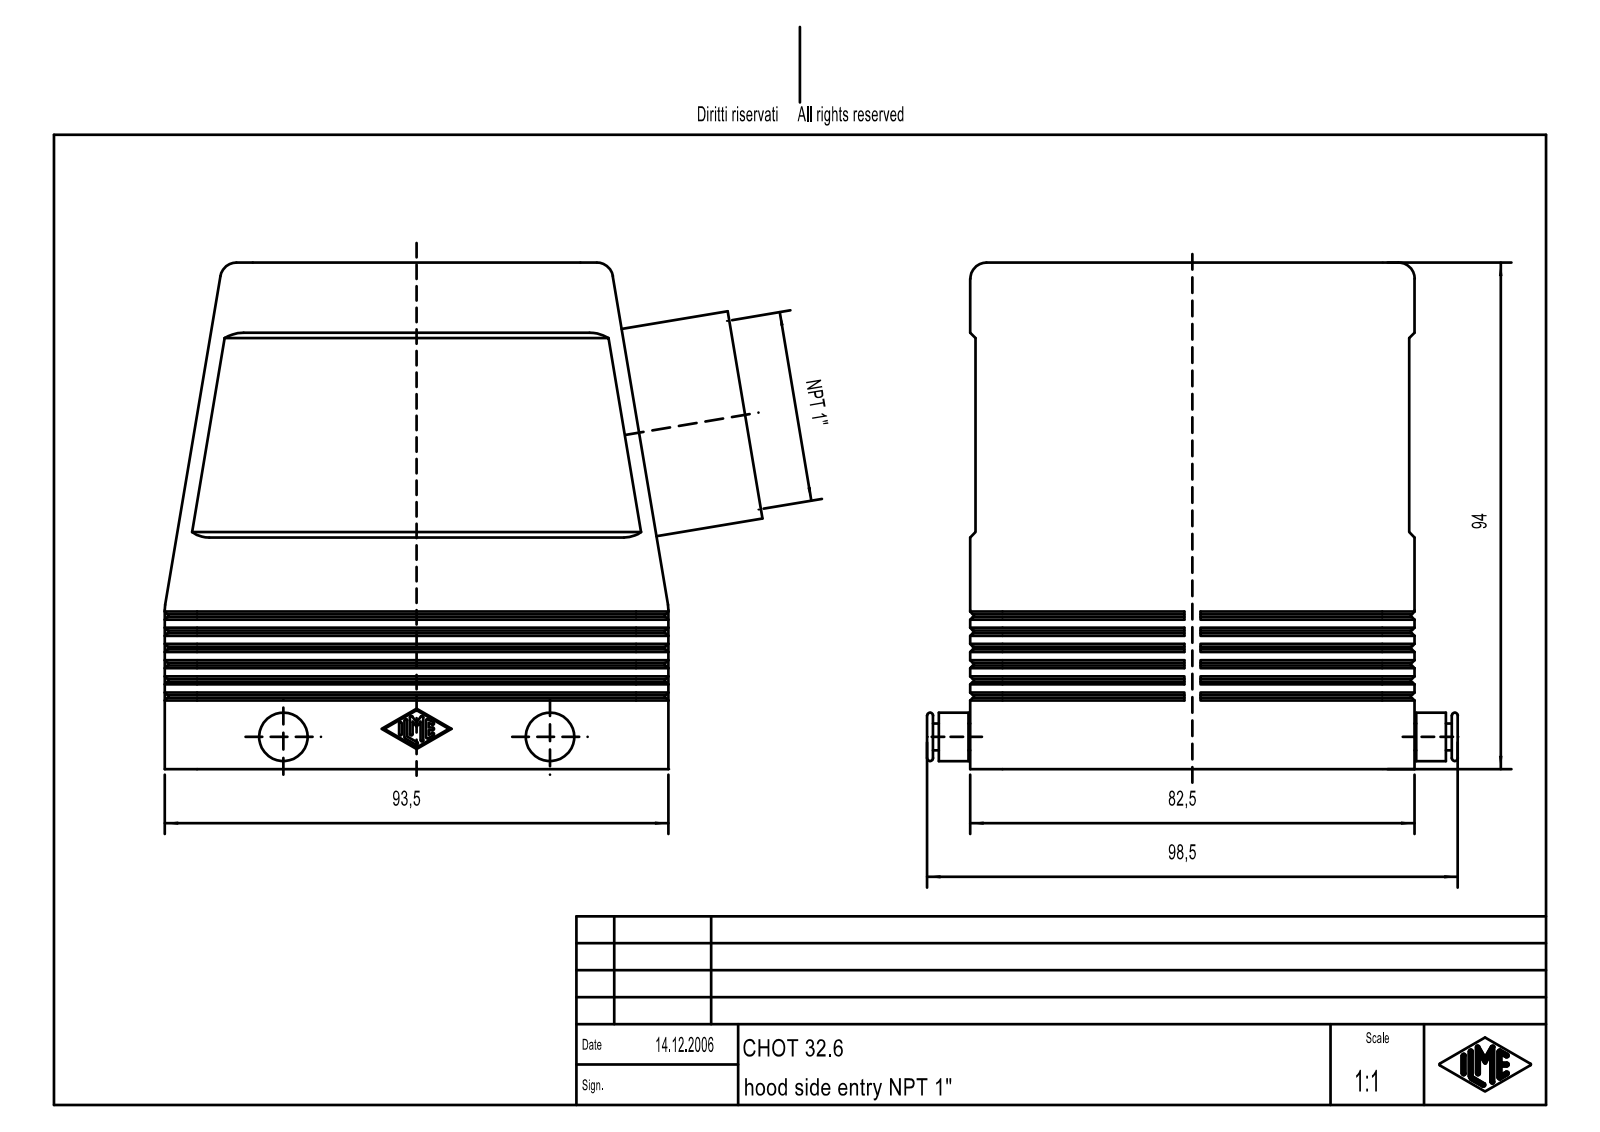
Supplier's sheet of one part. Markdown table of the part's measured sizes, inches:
| quantity | value |
| --- | --- |
| part name | MSBO10311 |
| STEP written by | Creo Elements/Direct Modeling 18.0B 02-Dec-2011 (C) Parametric Technology GmbH (AUTOMOTIVE_DESIGN) |
| units | inches |
| bodies | 1 solid, 519 faces (273 planar, 148 cylindrical, 98 other) |
| overall size | 4.369 × 3.878 × 3.701 |
| volume | 9.535 in³ |
| surface area | 123 in² |
| round holes (diameter × count) | 0.138 × 8, 0.097 × 6, 0.097 × 2 |
| round bosses / shafts (diameter × count) | 0.354 × 2, 0.197 × 2, 1.535 × 1 |
| partial cylindrical surfaces (radius × count) | 0.01 × 14, 0.079 × 12, 0.236 × 10, 0.118 × 4, 0.209 × 4, 0.768 × 1 |
| main face-to-face distances | 0.157, 3.091, 2.933, 3.248, 0.118, 0.039, 3.209, 3.051, 2.815, 0.433 |
| hole center spacings | 1.063, 1.378, 3.051, 3.231, 3.348, 0.315, 2.441, 3.067 |
